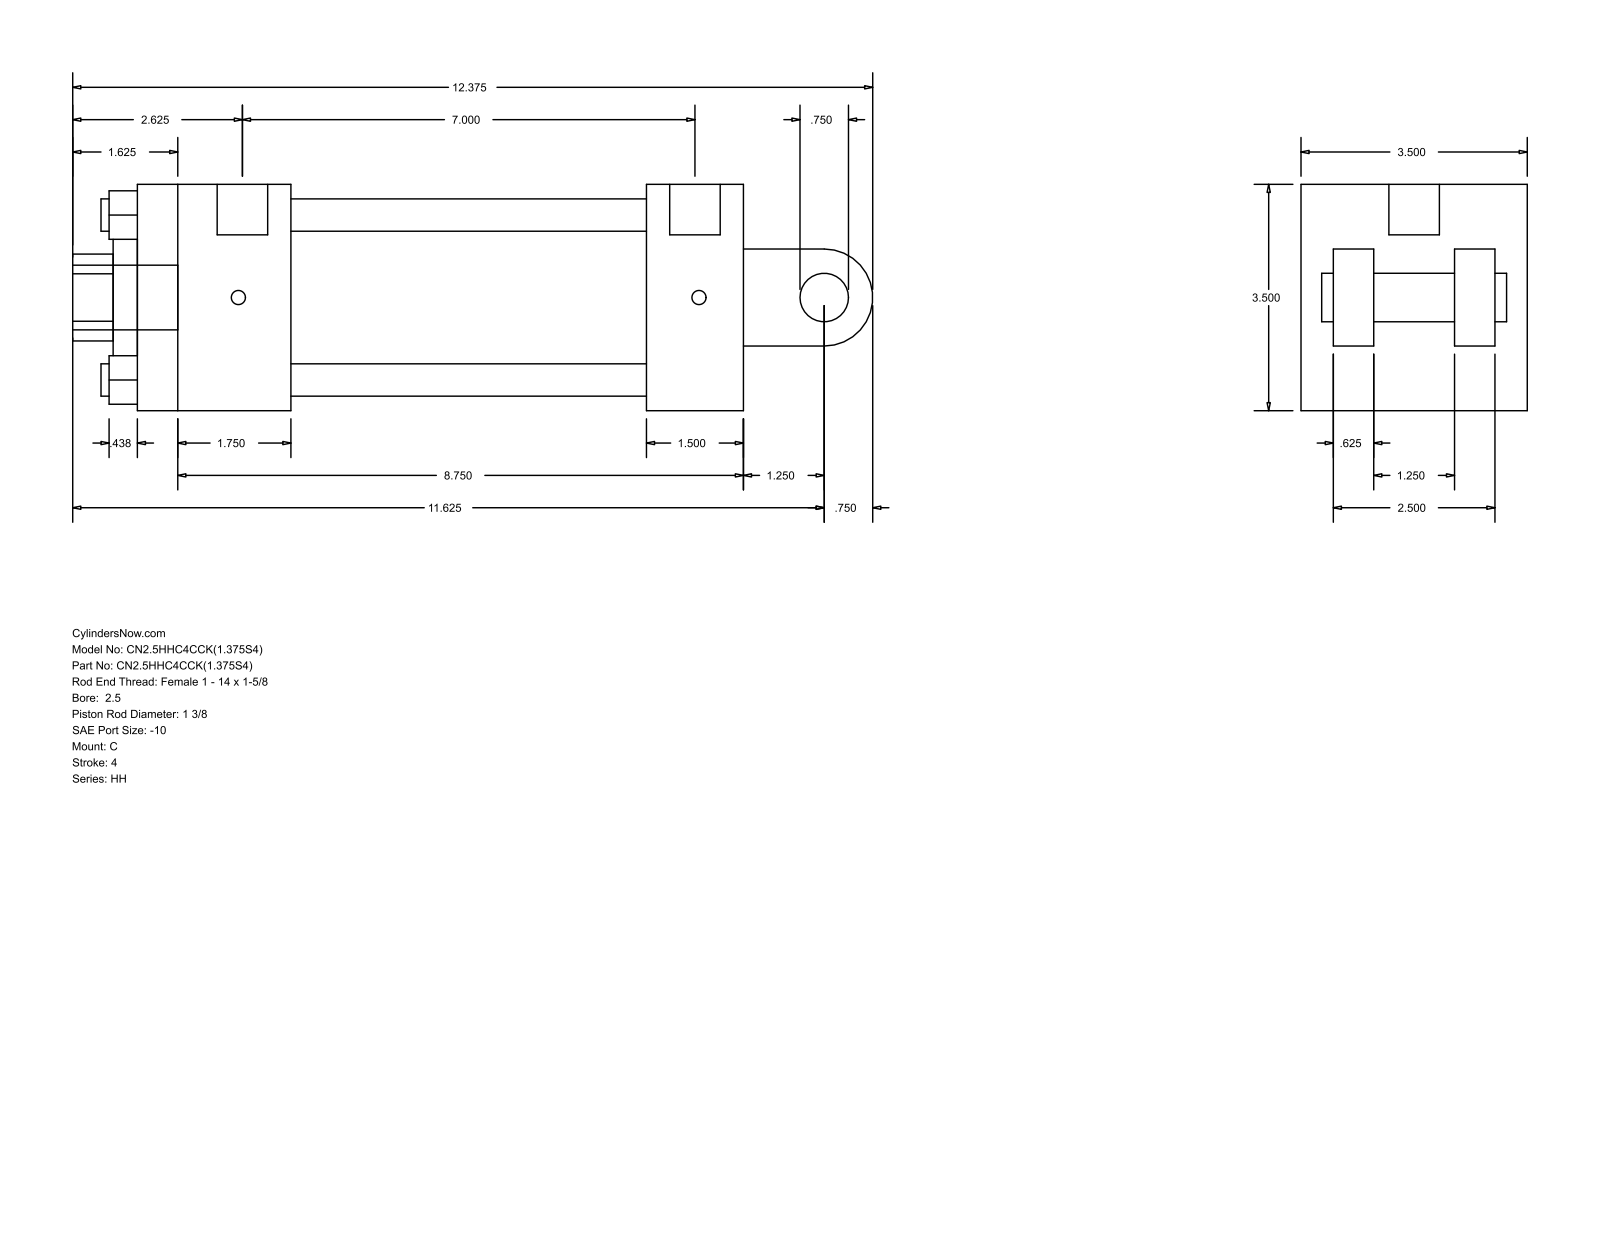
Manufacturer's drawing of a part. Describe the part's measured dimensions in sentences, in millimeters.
The part is named "HH_C__0250_1.375". Its 3-D file was written by "GSSL Pune (CONFIG_CONTROL_DESIGN)". It is 0 solids with 99 faces: 70 planar, 29 cylindrical and 0 other. Overall it measures 314.32 by 88.9 by 88.9 millimeters. Round holes: 4 of diameter 12.7, 2 of diameter 5.56, 1 of diameter 19.84, 1 of diameter 34.92, 1 of diameter 50.8, 1 of diameter 73.03. Round bosses or shafts: 2 of diameter 5.56, 1 of diameter 25.4, 1 of diameter 19.84, 1 of diameter 19.05. Partial cylindrical surfaces (rounded edges, fillets, slot ends): 1 of radius 17.06, 1 of radius 19.05. The main face-to-face distances are 88.9, 238.12, 63.5, 15.87, 12.7, 200.03, 38.09, 60.32, 139.71, 177.8. The hole center spacings are 45.79, 64.76, 91.58, 1.59.
